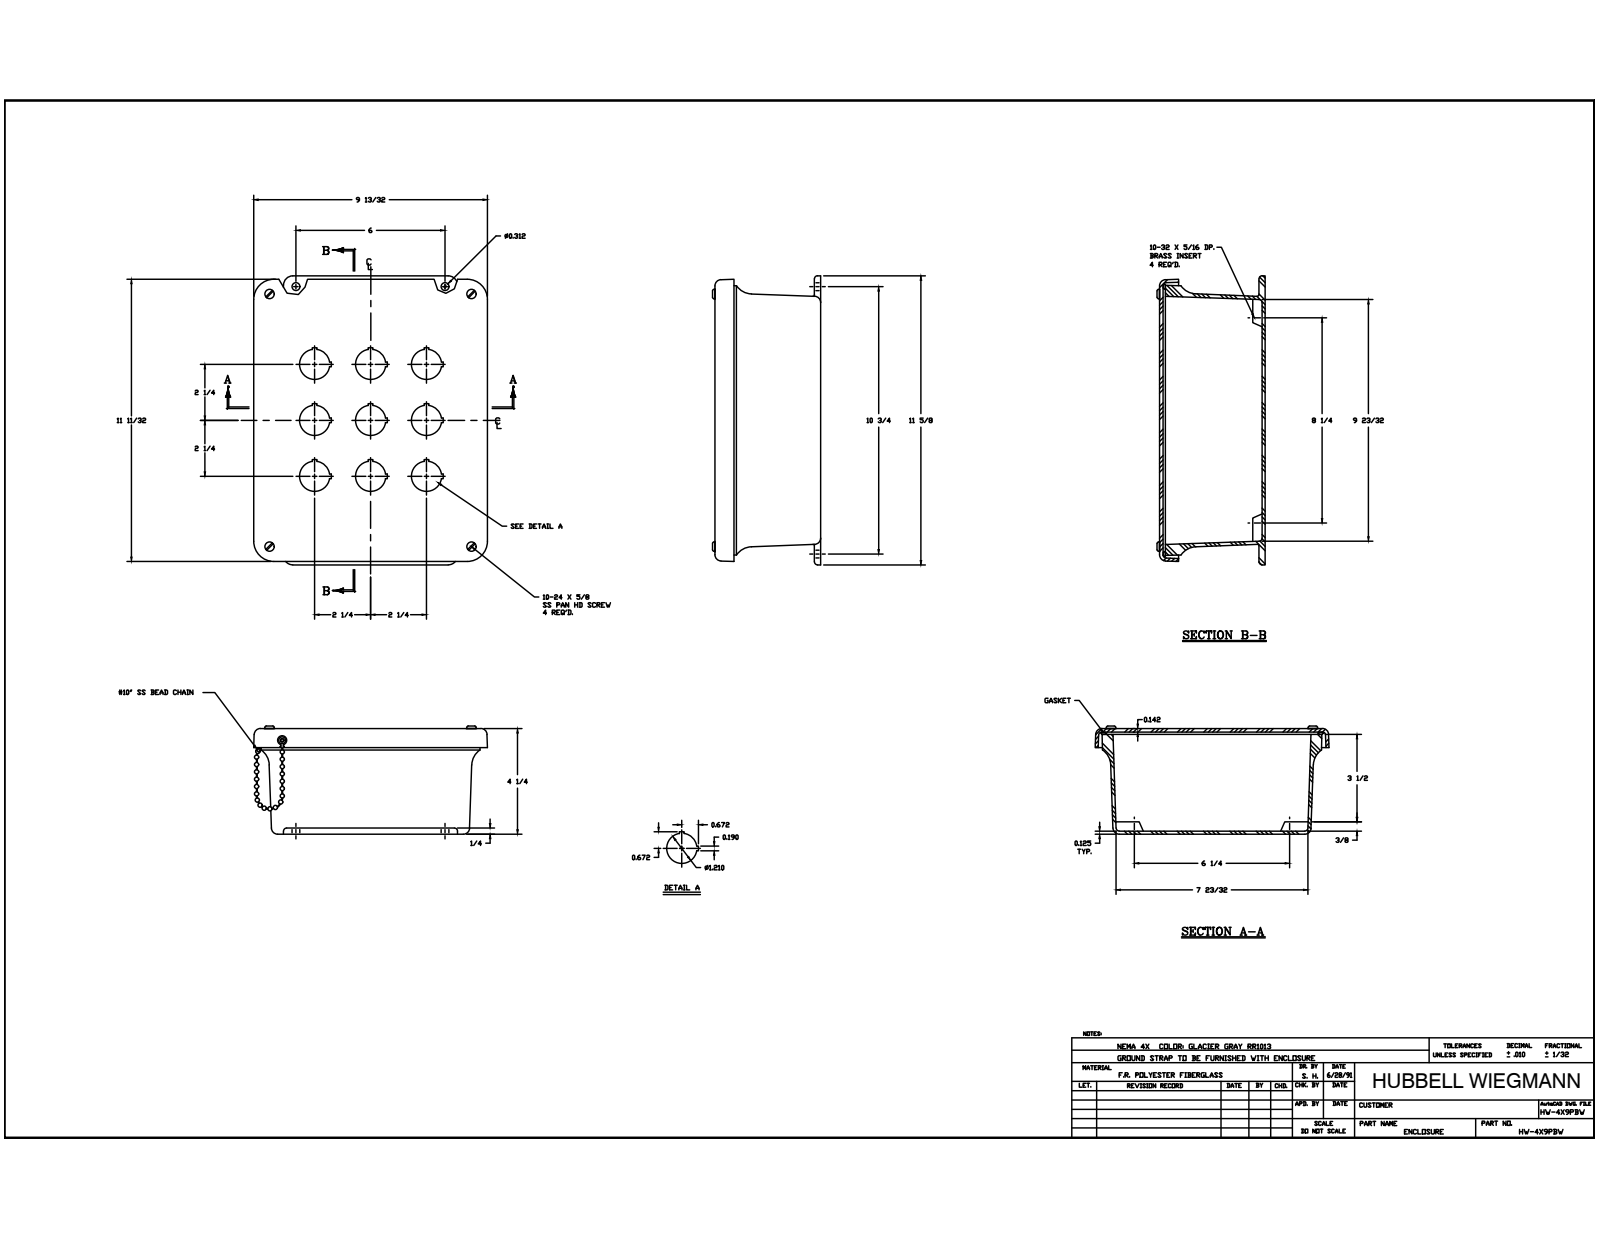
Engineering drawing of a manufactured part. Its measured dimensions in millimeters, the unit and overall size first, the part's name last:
Units: millimetres
Overall size (bounding box): 295.27 × 238.89 × 107.95
Round holes (diameter × count): ⌀30.73 ×9, ⌀3.68 ×4, ⌀3.96 ×4, ⌀5.56 ×4, ⌀6.35 ×4, ⌀7.14 ×4, ⌀7.94 ×4, ⌀3.56 ×2, ⌀2.64 ×1
Round bosses / shafts (diameter × count): ⌀7.14 ×4, ⌀5.54 ×4, ⌀0.74 ×2, ⌀9.4 ×1
Partial cylindrical surfaces — rounded edges, fillets, slot ends (radius × count): R0.79 ×36, R1.09 ×16, R3.17 ×16, R6.35 ×12, R7.98 ×4, R19.05 ×4, R0.79 ×2, R1.6 ×2
Main face-to-face distances: 107.95, 104.9, 3.05, 3.17, 101.73, 104.78, 3.19, 3.18, 101.98, 98.81
Hole centre spacings: 57.15, 80.82, 127.79, 31.91, 33.96, 114.3, 234.97, 241.32
Volume: 908 642 mm³ · Surface area: 482 949 mm²
Bodies: 15 solids, 541 faces (162 planar, 195 cylindrical, 184 other)
Part name (STEP PRODUCT): WPF9PBW BOX; 10-32 X0.3125 DP BRASS INSERT; 10-24X0.50 DP BRASS INSERT; SS BEAD CHAIN (+5 more)
STEP written by: Autodesk Inventor 2014 (AUTOMOTIVE_DESIGN)
